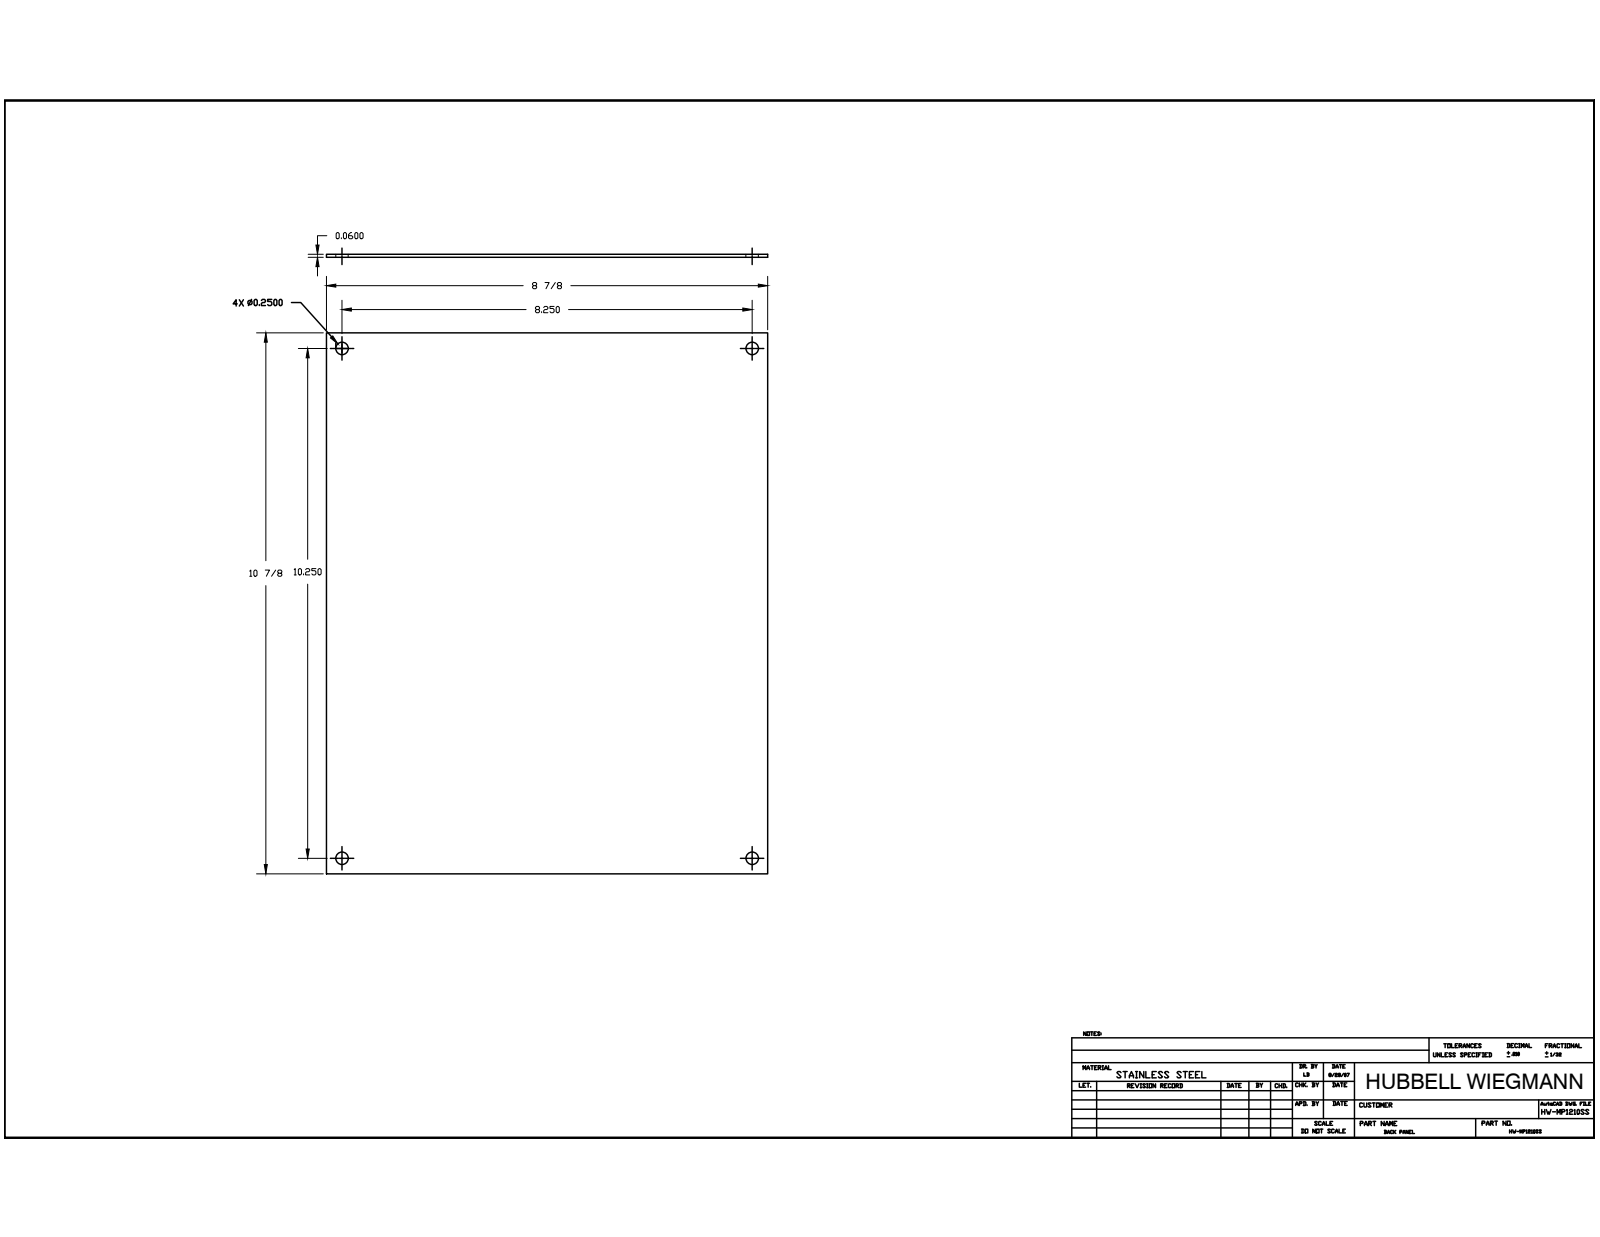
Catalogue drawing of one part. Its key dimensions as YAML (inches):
part_name: "BP1210SS_STP"
step_written_by: "Autodesk Inventor 2014 (AUTOMOTIVE_DESIGN)"
units: inches
bodies: {solids: 1, faces: 10, planar: 6, cylindrical: 4, other: 0}
overall_size: [10.875, 8.875, 0.06]
volume: 5.779
surface_area: 195.2
round_holes:
  - {diameter: 0.25, count: 4}
face_to_face_distances: [0.06, 8.875, 10.875]
hole_center_spacings: [8.25, 10.25, 13.157]
